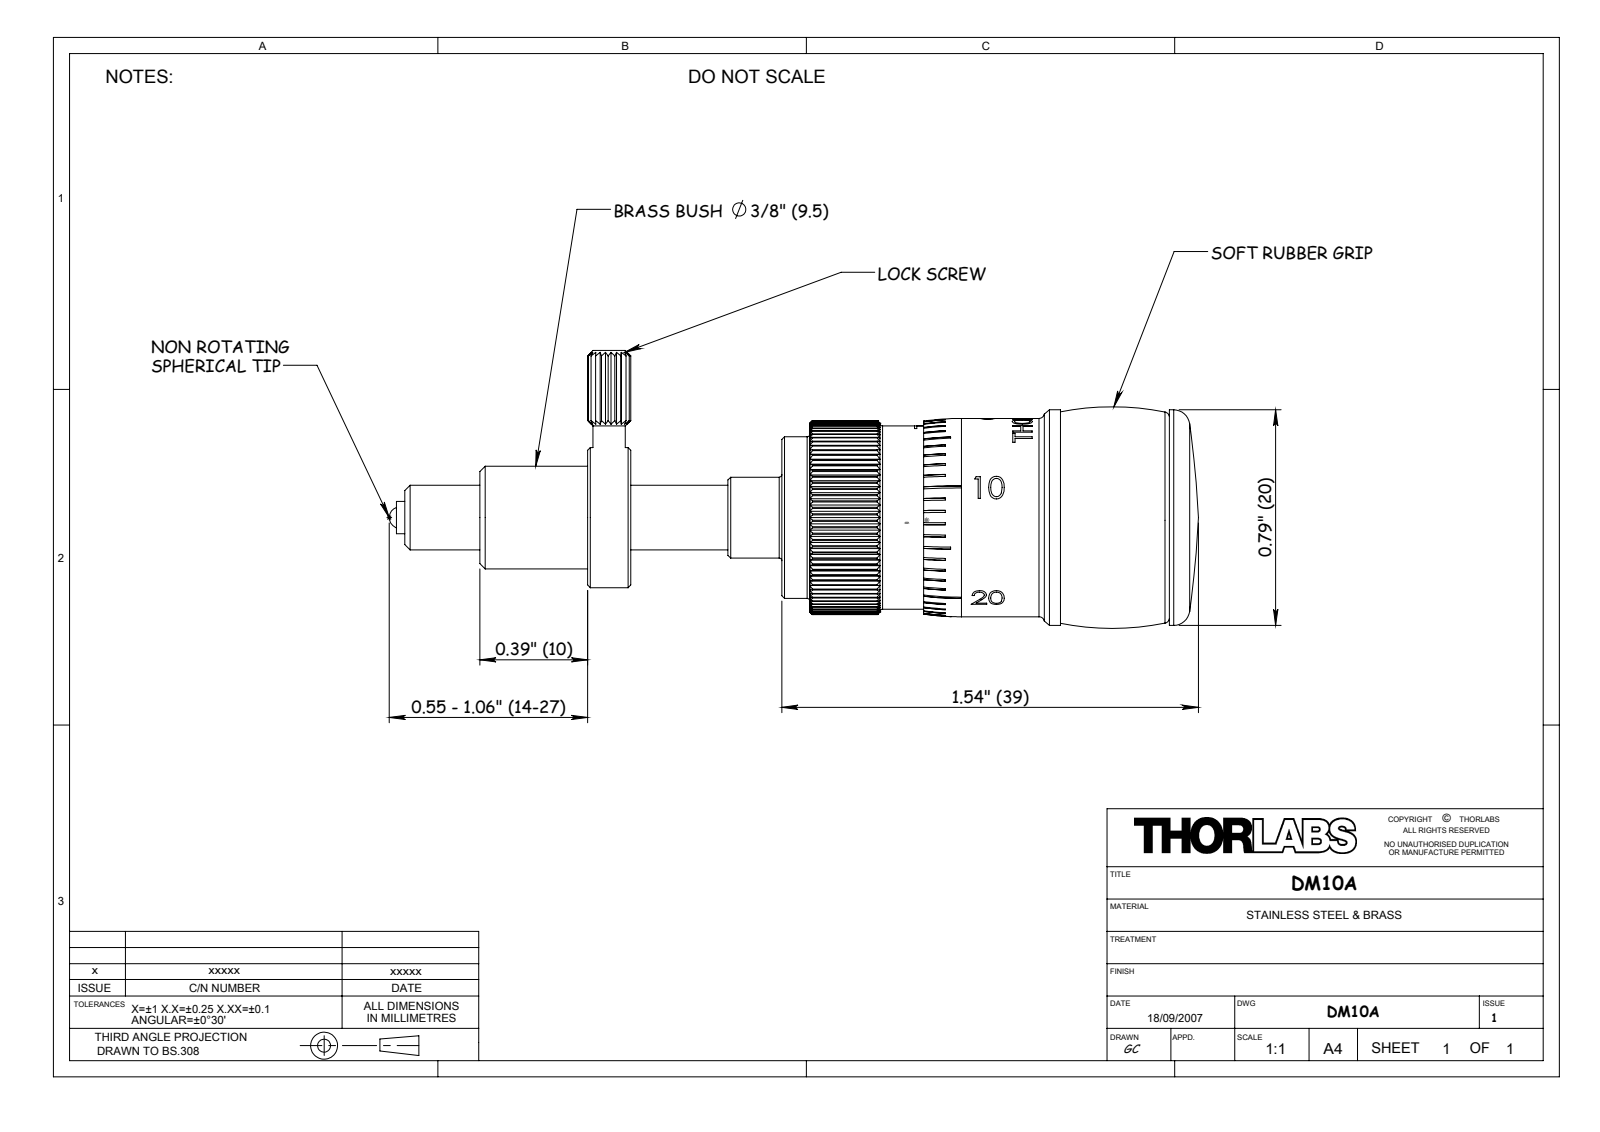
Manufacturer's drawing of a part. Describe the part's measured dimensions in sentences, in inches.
The part is named "17068-E0W". Its 3-D file was written by "SolidWorks 2007 (AUTOMOTIVE_DESIGN)". It is 8 solids with 916 faces: 402 planar, 187 cylindrical and 327 other. Overall it measures 2.957 by 1.015 by 0.809 inches. Its volume is 0.479 cubic inches and its surface area 13.98 square inches. Round holes: 2 of diameter 0.098, 1 of diameter 0.063, 1 of diameter 0.079, 1 of diameter 0.157, 1 of diameter 0.217, 1 of diameter 0.504, 1 of diameter 0.551, 1 of diameter 0.591, 1 of diameter 0.606, 1 of diameter 0.677. Round bosses or shafts: 2 of diameter 0.118, 1 of diameter 0.787, 1 of diameter 0.724, 1 of diameter 0.669, 1 of diameter 0.614, 1 of diameter 0.512, 1 of diameter 0.375, 1 of diameter 0.295. Partial cylindrical surfaces (rounded edges, fillets, slot ends): 1 of radius 0.043, 1 of radius 0.354. The main face-to-face distances are 0.079, 0.487, 1.135, 1.214, 1.767, 0.631, 0.552, 0.468, 0.668, 0.746. The hole center spacings are 1.956.
